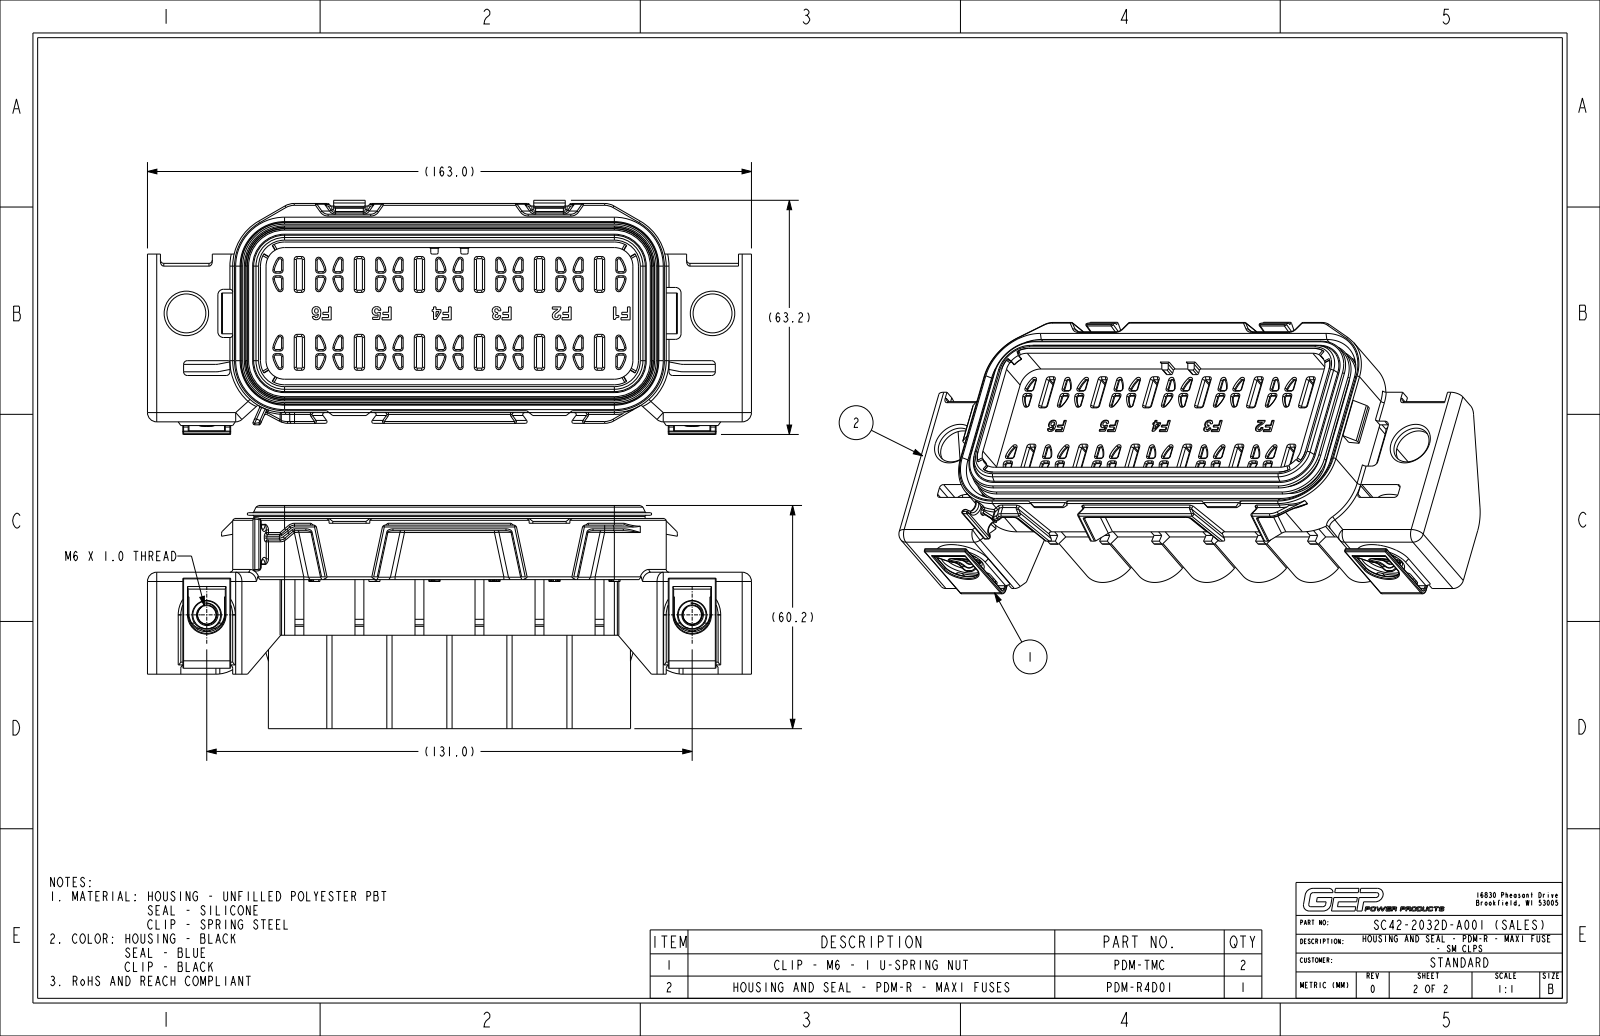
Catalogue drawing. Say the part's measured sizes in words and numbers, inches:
The part is named "C26-1012-2D_SALES_NCF; C14-1013_INSTALLED_NCF; PDM-RS_INSTALLED_NCF_ASM; PDM-R4D01_NCF_ASM (+3 more)". Its 3-D file was written by "CREO PARAMETRIC BY PTC INC, 2024014 (CONFIG_CONTROL_DESIGN)". It is 4 solids with 3619 faces: 1729 planar, 995 cylindrical and 895 other. Overall it measures 6.417 by 2.487 by 2.37 inches. Its volume is 9.341 cubic inches and its surface area 182.2 square inches. Round holes: 12 of diameter 0.541, 4 of diameter 0.413, 2 of diameter 0.197, 2 of diameter 0.295, 2 of diameter 0.492. Round bosses or shafts: 5 of diameter 0.25, 2 of diameter 0.276, 1 of diameter 0.197, 1 of diameter 0.098. Partial cylindrical surfaces (rounded edges, fillets, slot ends): 157 of radius 0.016, 148 of radius 0.02, 116 of radius 0.008, 47 of radius 0.031, 46 of radius 0.012, 39 of radius 0.035, 26 of radius 0.039, 16 of radius 0.014. The main face-to-face distances are 0.079, 0.638, 1.516, 0.059, 0.374, 0.098, 1.276, 0.276, 0.453, 1.457. The hole center spacings are 0.638, 1.044, 1.276, 1.52, 0.827, 1.913, 2.084, 1.27.
